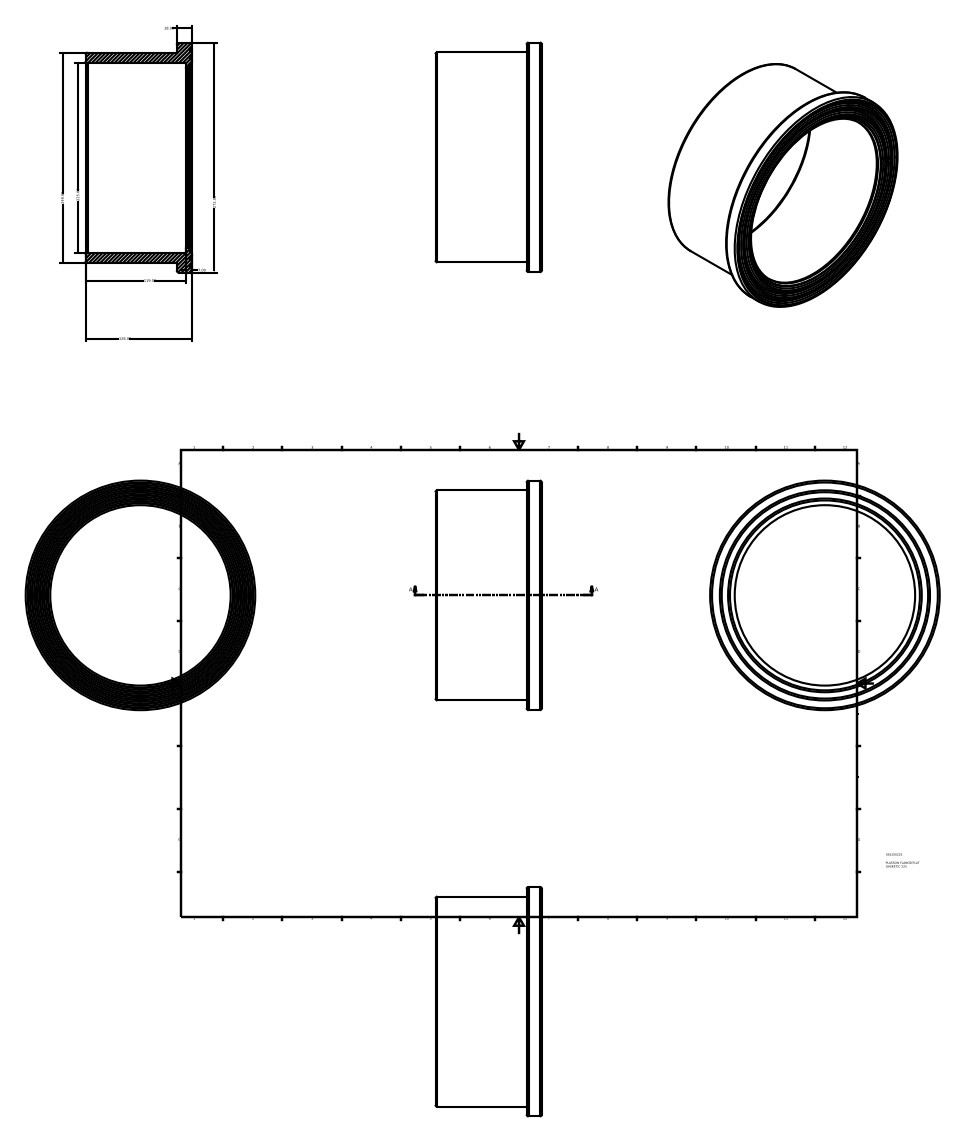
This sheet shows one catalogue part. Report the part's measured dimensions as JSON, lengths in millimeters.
{"part_name": "055200225", "step_written_by": "Autodesk Inventor 2015 (AUTOMOTIVE_DESIGN)", "units": "millimeters", "bodies": {"solids": 1, "faces": 28, "planar": 9, "cylindrical": 4, "other": 15}, "overall_size": [272, 272, 126], "volume_mm3": 1288000, "surface_area_mm2": 231744, "round_holes": [[213.75, 1], [225, 1]], "round_bosses_or_shafts": [[272, 1], [249, 1]], "face_to_face_distances": [108, 119, 11, 123.3, 15.3, 4.3, 126, 18, 7, 2.7]}
